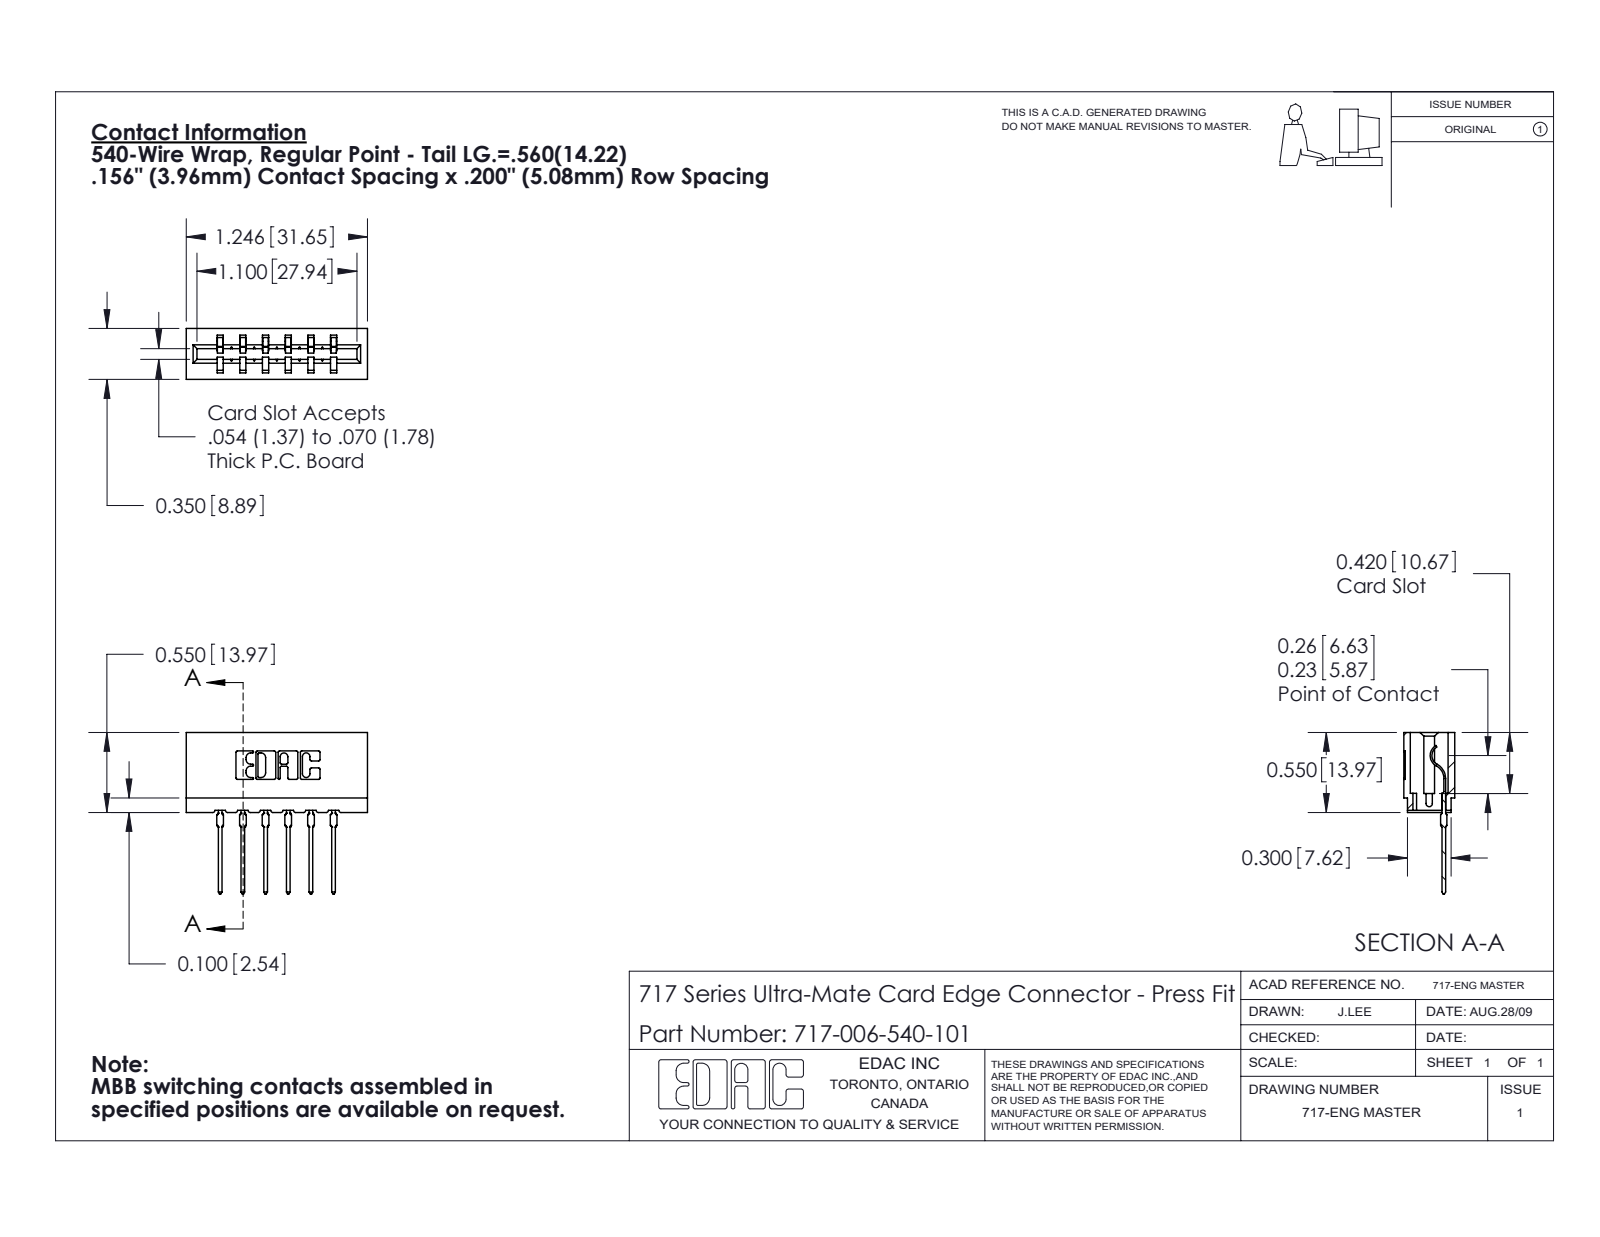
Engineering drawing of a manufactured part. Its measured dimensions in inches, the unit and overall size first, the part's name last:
Units: inches
Overall size (bounding box): 1.246 × 1.109 × 0.35
Partial cylindrical surfaces — rounded edges, fillets, slot ends (radius × count): R0.01 ×22, R0.015 ×12, R0.021 ×12, R0.007 ×6, R0.031 ×6, R0.005 ×4, R0.011 ×4, R0.026 ×3
Main face-to-face distances: 0.212, 0.156, 0.138, 0.35, 0.198, 0.312, 0.468, 0.624, 0.042, 0.312
Volume: 0.174 in³ · Surface area: 5.705 in²
Bodies: 7 solids, 772 faces (462 planar, 154 cylindrical, 156 other)
Part name (STEP PRODUCT): 717-006-540-101; 745-292-001_540; 717 Part_Insulator Option - 06
STEP written by: SolidWorks 2020 (CONFIG_CONTROL_DESIGN)
